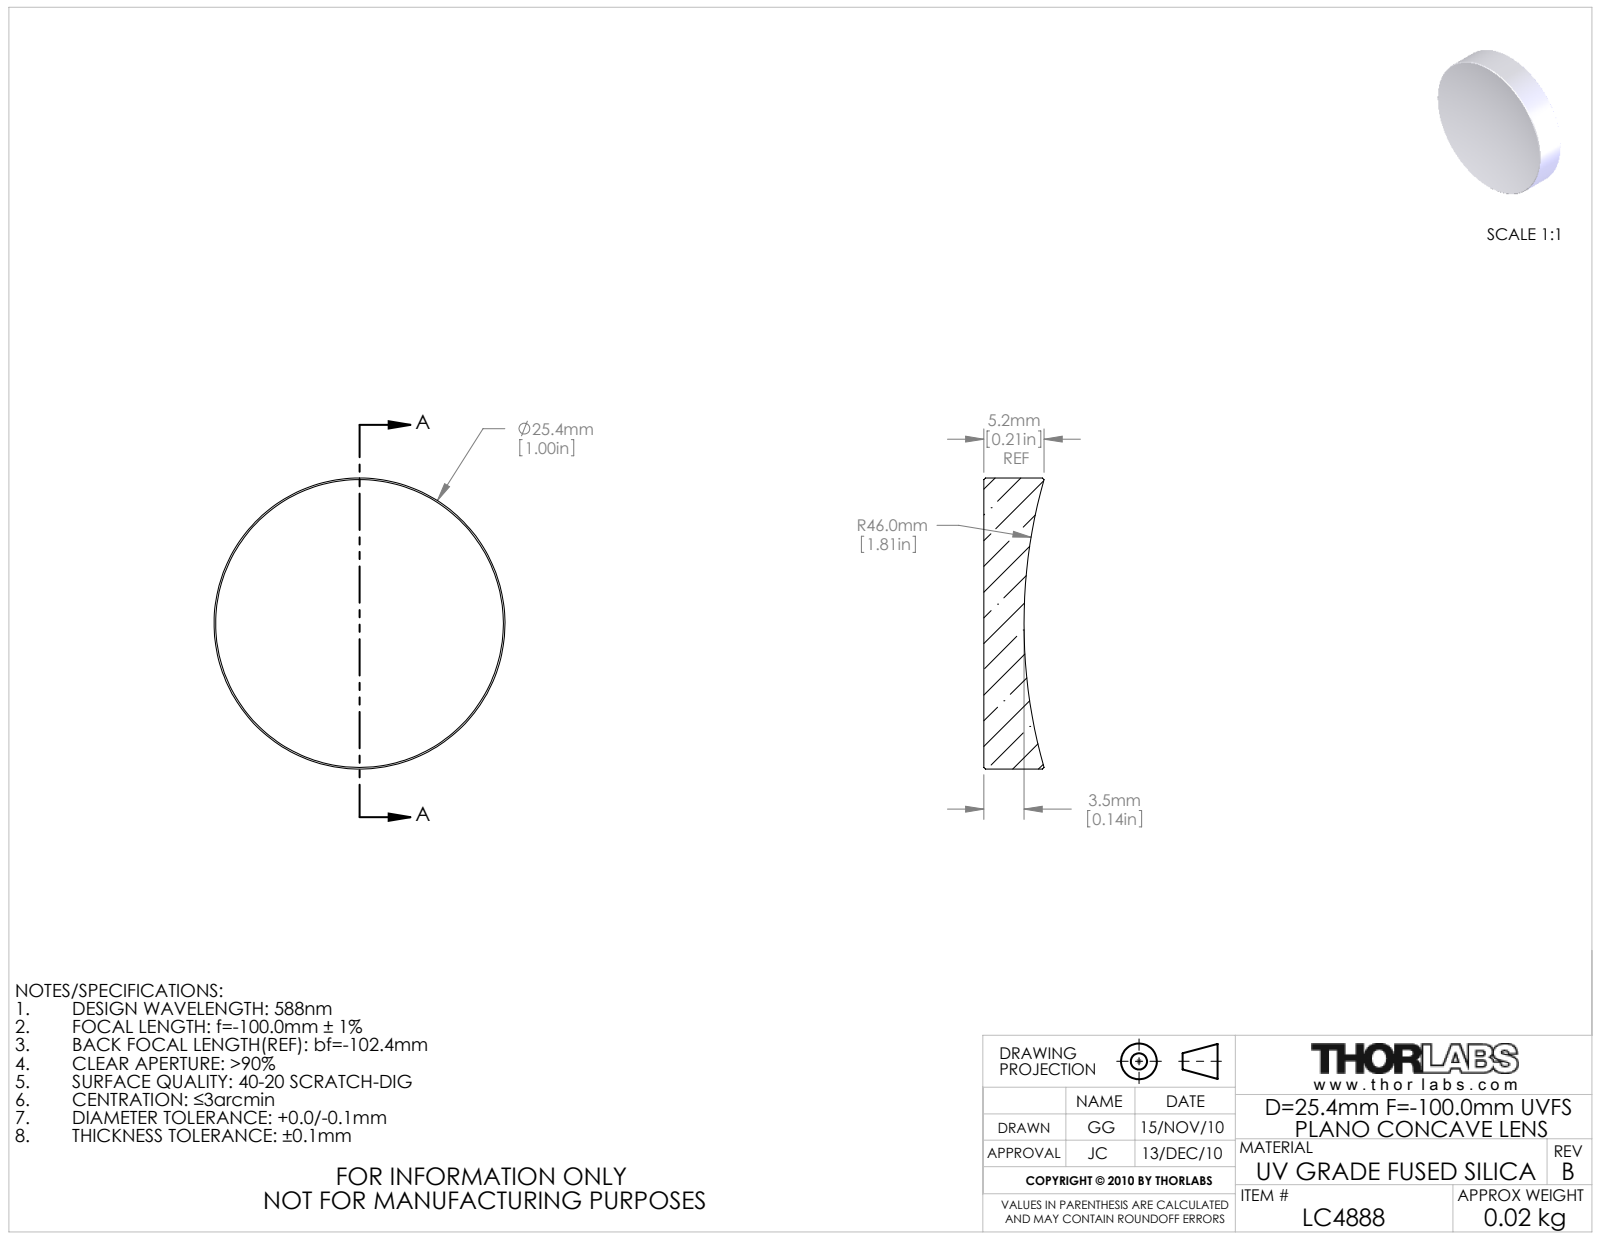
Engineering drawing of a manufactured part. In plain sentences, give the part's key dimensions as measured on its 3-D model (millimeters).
The part is named "3504-E0W". Its 3-D file was written by "SolidWorks 2009 (AUTOMOTIVE_DESIGN)". It is 1 solid with 9 faces: 1 planar, 2 cylindrical and 6 other. Overall it measures 25.4 by 25.4 by 5.25 millimeters. Its volume is 2 222 cubic millimeters and its surface area 1 428 square millimeters. Round bosses or shafts: 1 of diameter 25.4.
